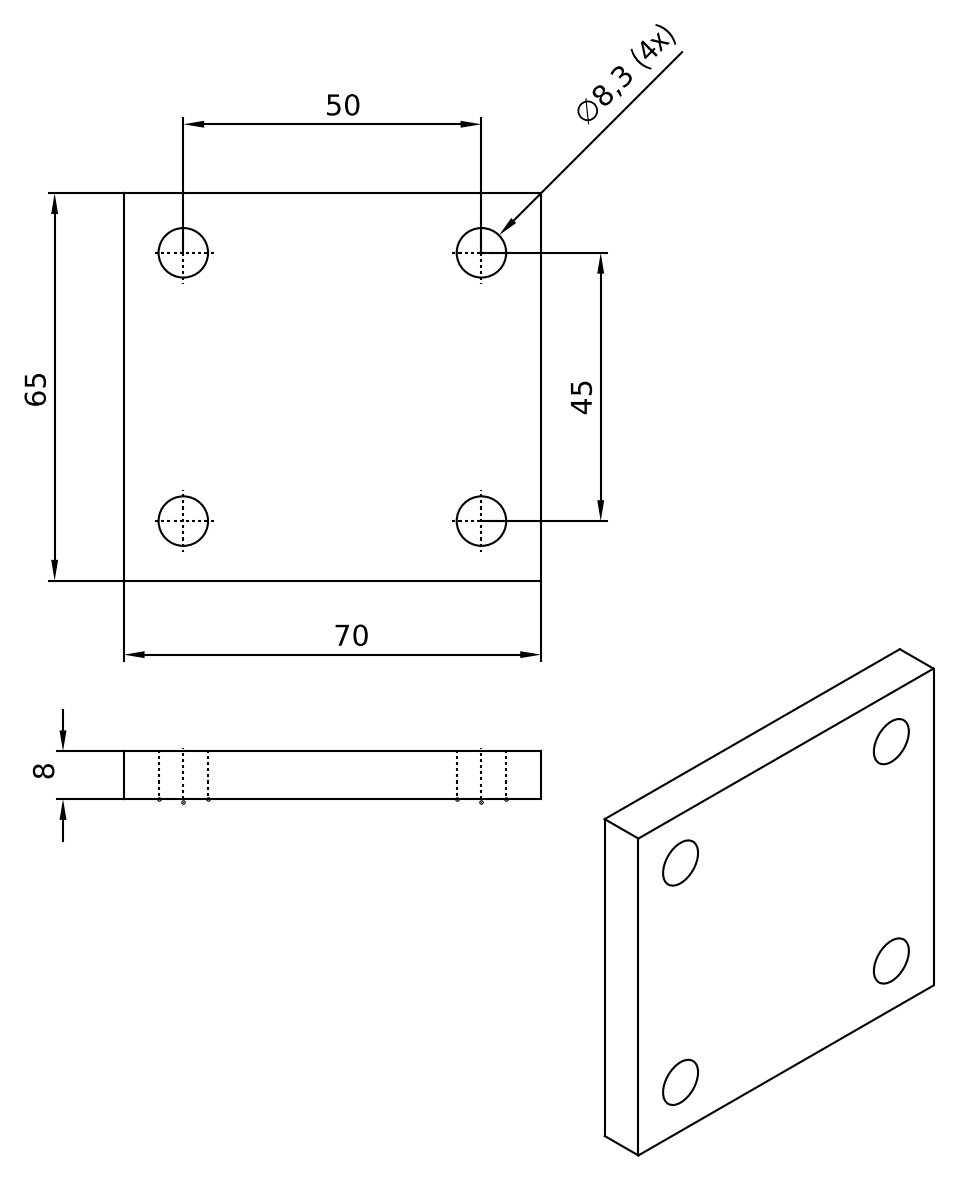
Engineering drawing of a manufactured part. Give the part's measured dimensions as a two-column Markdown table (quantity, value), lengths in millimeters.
| quantity | value |
| --- | --- |
| part name | 616-25E1 |
| STEP written by | Autodesk Inventor 8 (AUTOMOTIVE_DESIGN) |
| units | millimeters |
| bodies | 1 solid, 14 faces (6 planar, 0 cylindrical, 8 other) |
| overall size | 70 × 65 × 8 |
| volume | 34 669 mm³ |
| surface area | 11 661 mm² |
| main face-to-face distances | 8, 65, 70 |
